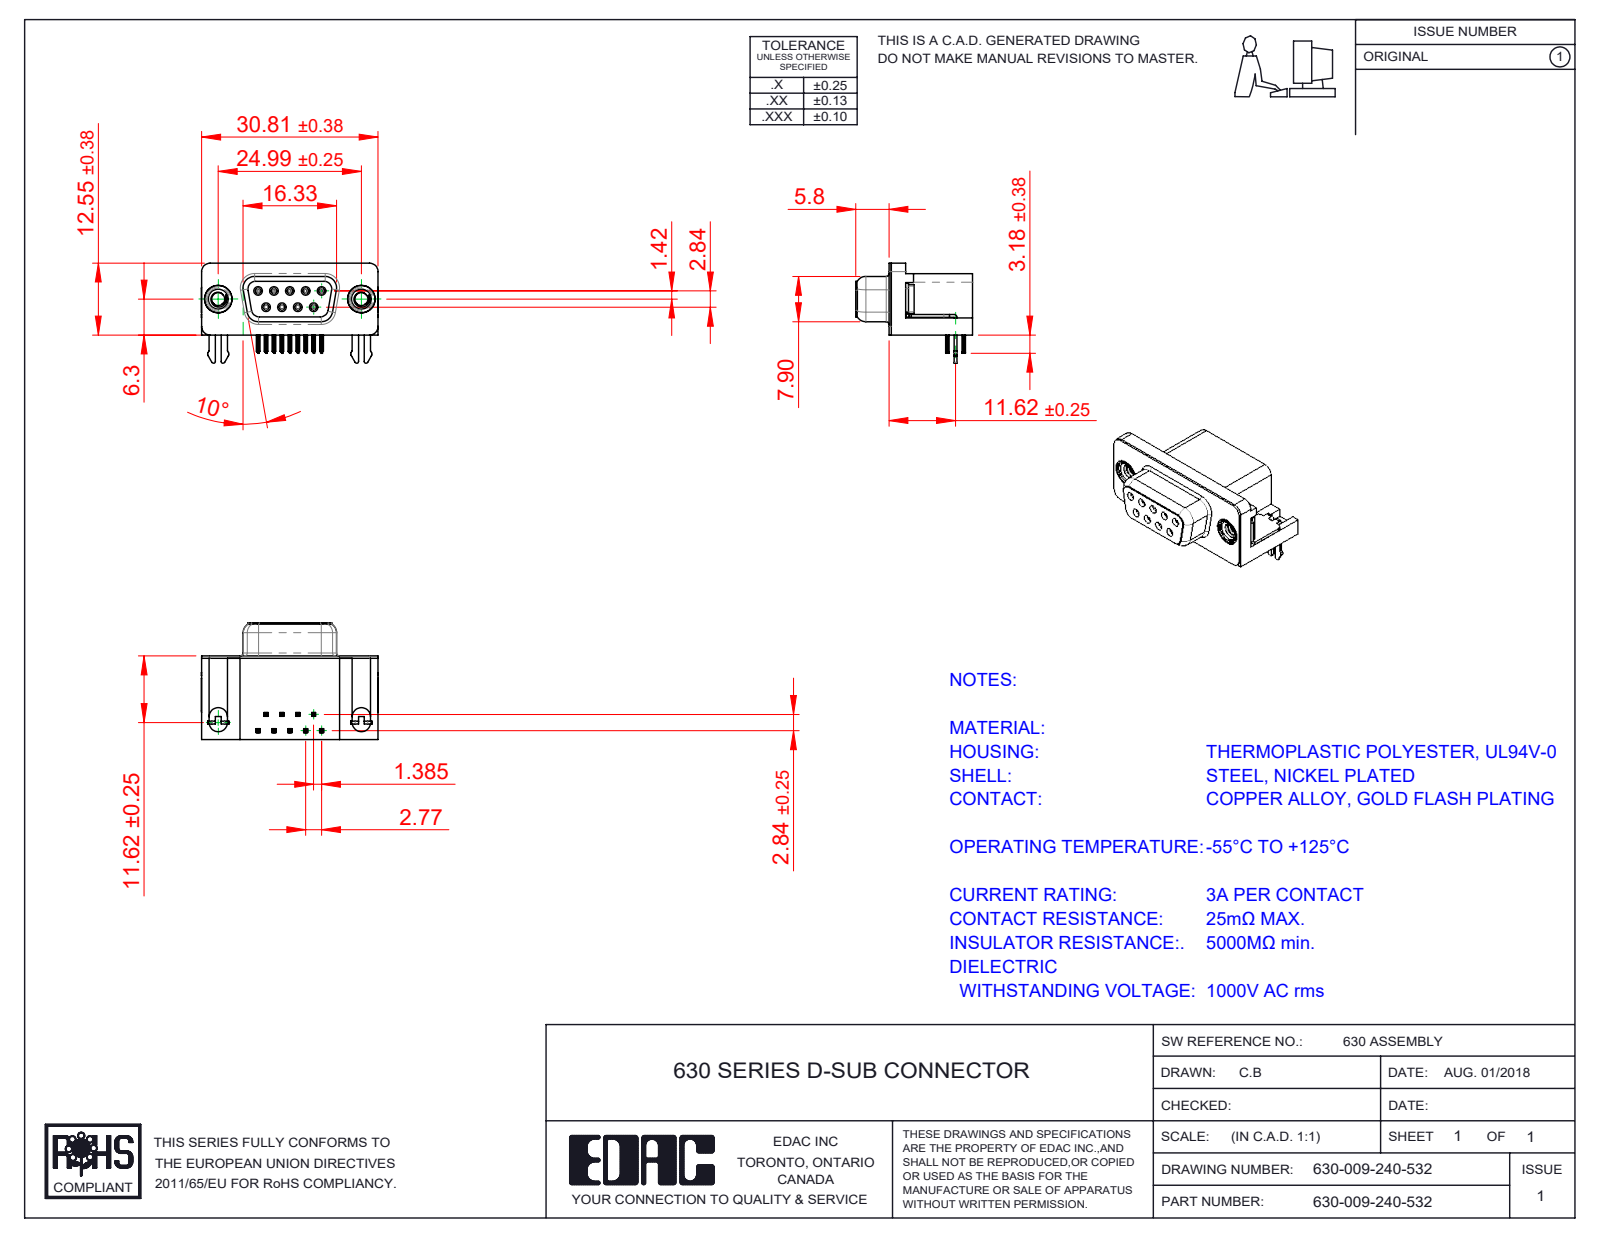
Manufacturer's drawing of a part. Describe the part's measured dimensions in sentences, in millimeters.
The part is named "630-009-240-532; 630 2 Prong Board Lock; 630 Housing_09 Socket; 630 Contact Bottom (+3 more)". Its 3-D file was written by "SolidWorks 2020 (CONFIG_CONTROL_DESIGN)". It is 15 solids with 1610 faces: 714 planar, 424 cylindrical and 472 other. Overall it measures 30.89 by 20.4 by 17.48 millimeters. Its volume is 4 206 cubic millimeters and its surface area 5 454 square millimeters. Round holes: 9 of diameter 0.8, 9 of diameter 0.9, 2 of diameter 2.26, 2 of diameter 4, 2 of diameter 4.8, 2 of diameter 5. Round bosses or shafts: 9 of diameter 1.2, 2 of diameter 4.9, 2 of diameter 4.75, 2 of diameter 3.9. Partial cylindrical surfaces (rounded edges, fillets, slot ends): 72 of radius 0.1, 36 of radius 0.15, 18 of radius 0.35, 18 of radius 1, 10 of radius 0.5, 9 of radius 0.34, 8 of radius 0.25, 8 of radius 1.35. The main face-to-face distances are 0.4, 14.6, 14.2, 10.34, 0.5, 6.2, 2.9, 2.5, 11.7, 0.35. The hole center spacings are 3.16, 2.77, 5.54, 5.03, 5.04, 8.31, 7.48, 7.49.
